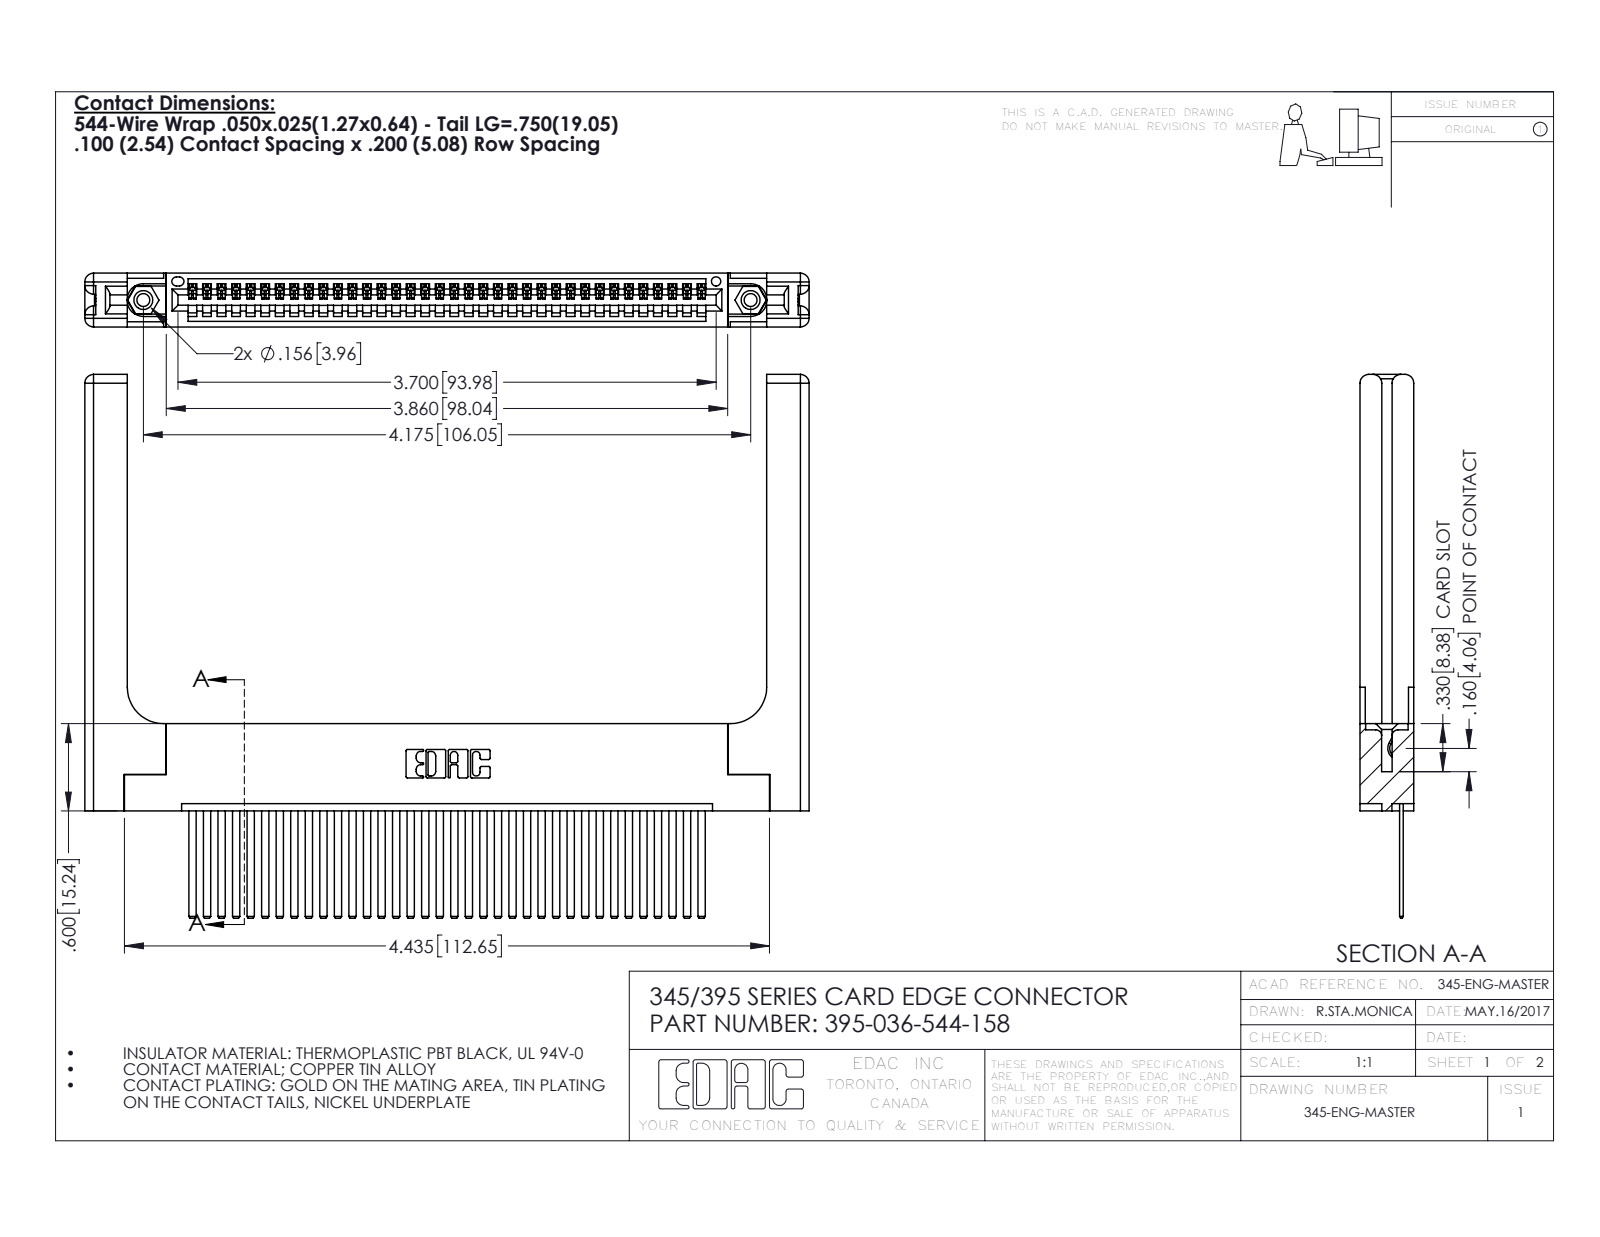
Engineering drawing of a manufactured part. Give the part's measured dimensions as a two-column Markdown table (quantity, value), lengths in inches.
| quantity | value |
| --- | --- |
| part name | 395-036-544-158; 345-250-001_345-250-001-102; 345-220-058_345-220-058; 345-292-001_345-293-144 (+1 more) |
| STEP written by | SolidWorks 2016 (CONFIG_CONTROL_DESIGN) |
| units | inches |
| bodies | 41 solids, 2254 faces (1524 planar, 670 cylindrical, 60 other) |
| overall size | 4.979 × 3.737 × 0.37 |
| volume | 1.274 in³ |
| surface area | 35.54 in² |
| round holes (diameter × count) | 0.089 × 2, 0.125 × 2, 0.156 × 2, 0.064 × 1 |
| round bosses / shafts (diameter × count) | 0.155 × 2 |
| partial cylindrical surfaces (radius × count) | 0.006 × 72, 0.01 × 22, 0.06 × 16, 0.007 × 6, 0.031 × 6, 0.026 × 3, 0.03 × 2, 0.031 × 2 |
| main face-to-face distances | 0.072, 0.298, 0.37, 0.098, 0.272, 0.025, 0.2, 0.148, 0.15, 0.225 |
| hole center spacings | 0.27, 3.939, 4.175 |
